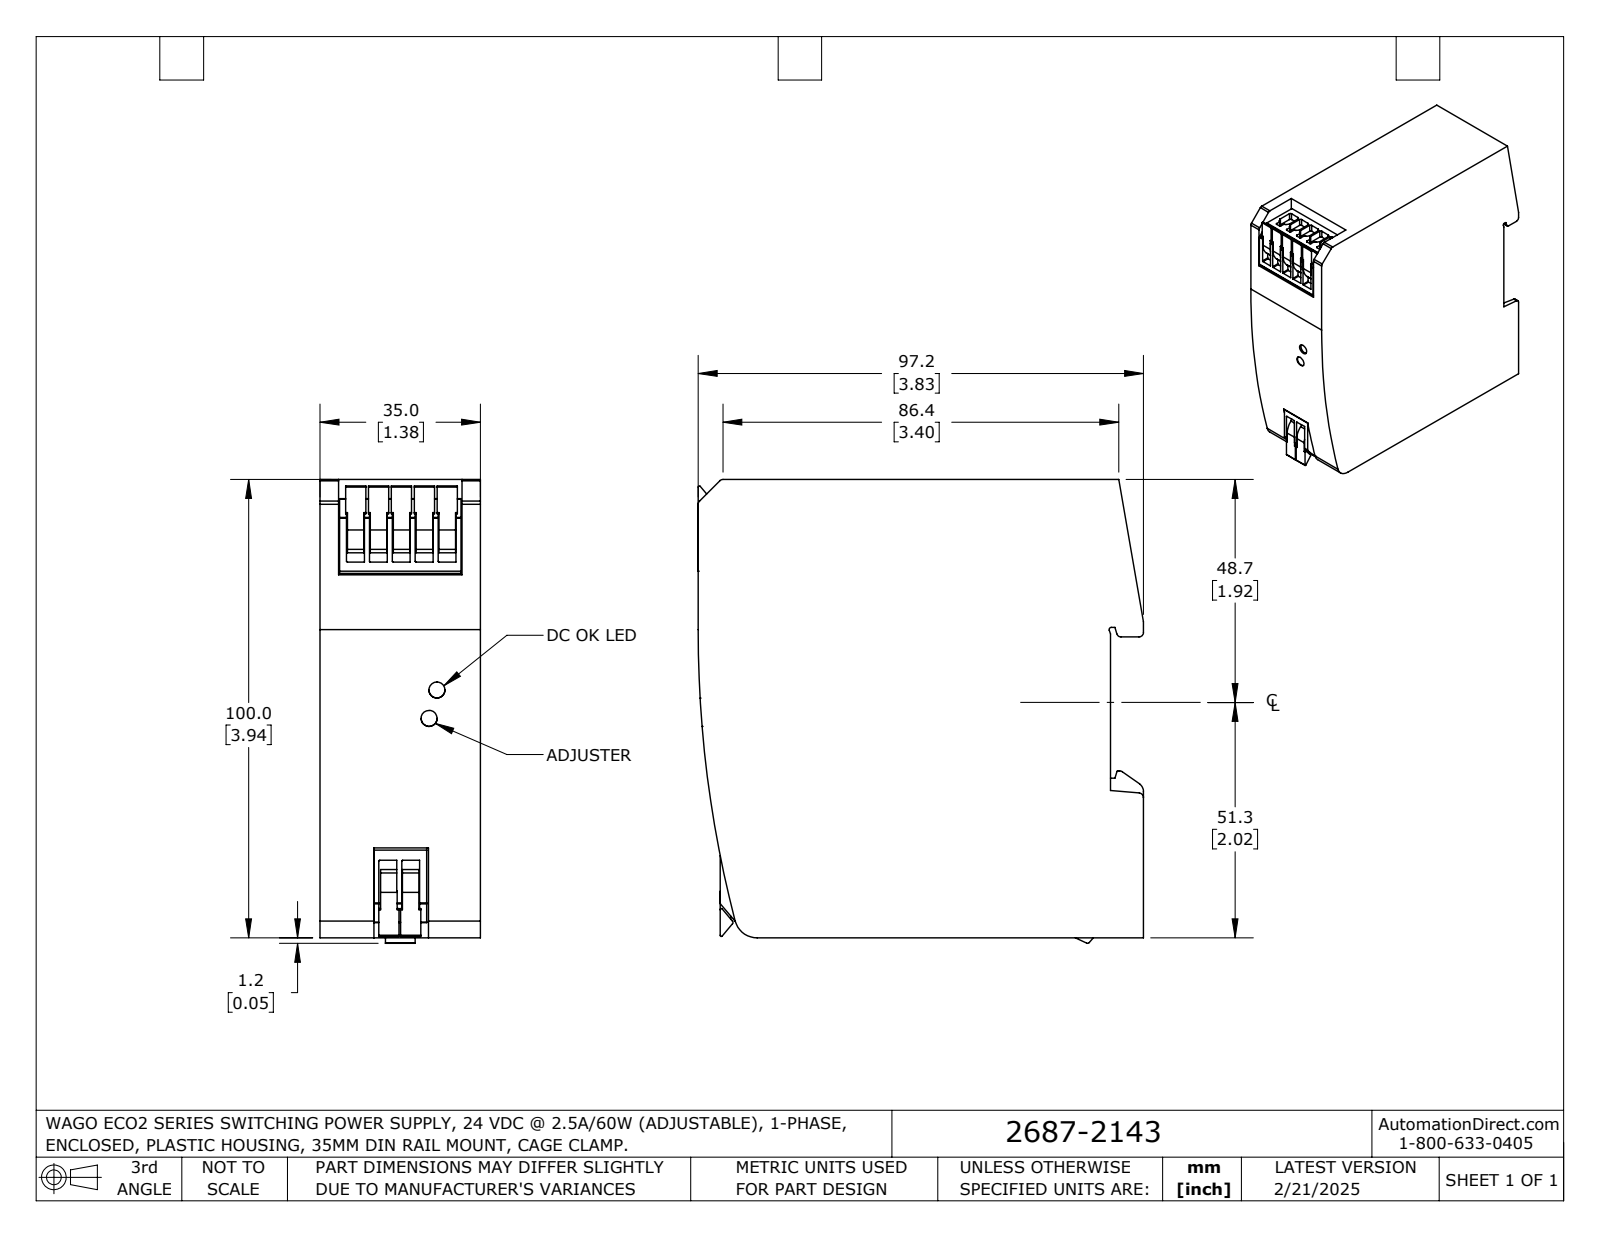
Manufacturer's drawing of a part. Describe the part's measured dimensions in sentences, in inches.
The part is named "2687-2143_HI". Its 3-D file was written by "SolidWorks 2024 (AUTOMOTIVE_DESIGN)". It is 1 solid with 383 faces: 233 planar, 150 cylindrical and 0 other. Overall it measures 3.984 by 3.827 by 1.378 inches. Its volume is 19.18 cubic inches and its surface area 59.19 square inches. Partial cylindrical surfaces (rounded edges, fillets, slot ends): 44 of radius 0.02, 18 of radius 0.012, 14 of radius 0.008, 8 of radius 0.008, 7 of radius 0.039, 4 of radius 0.01, 2 of radius 0.016, 2 of radius 0.063. The main face-to-face distances are 1.378, 3.937, 3.543, 3.827, 0.283, 0.304, 0.757, 0.295, 0.747, 0.285.
